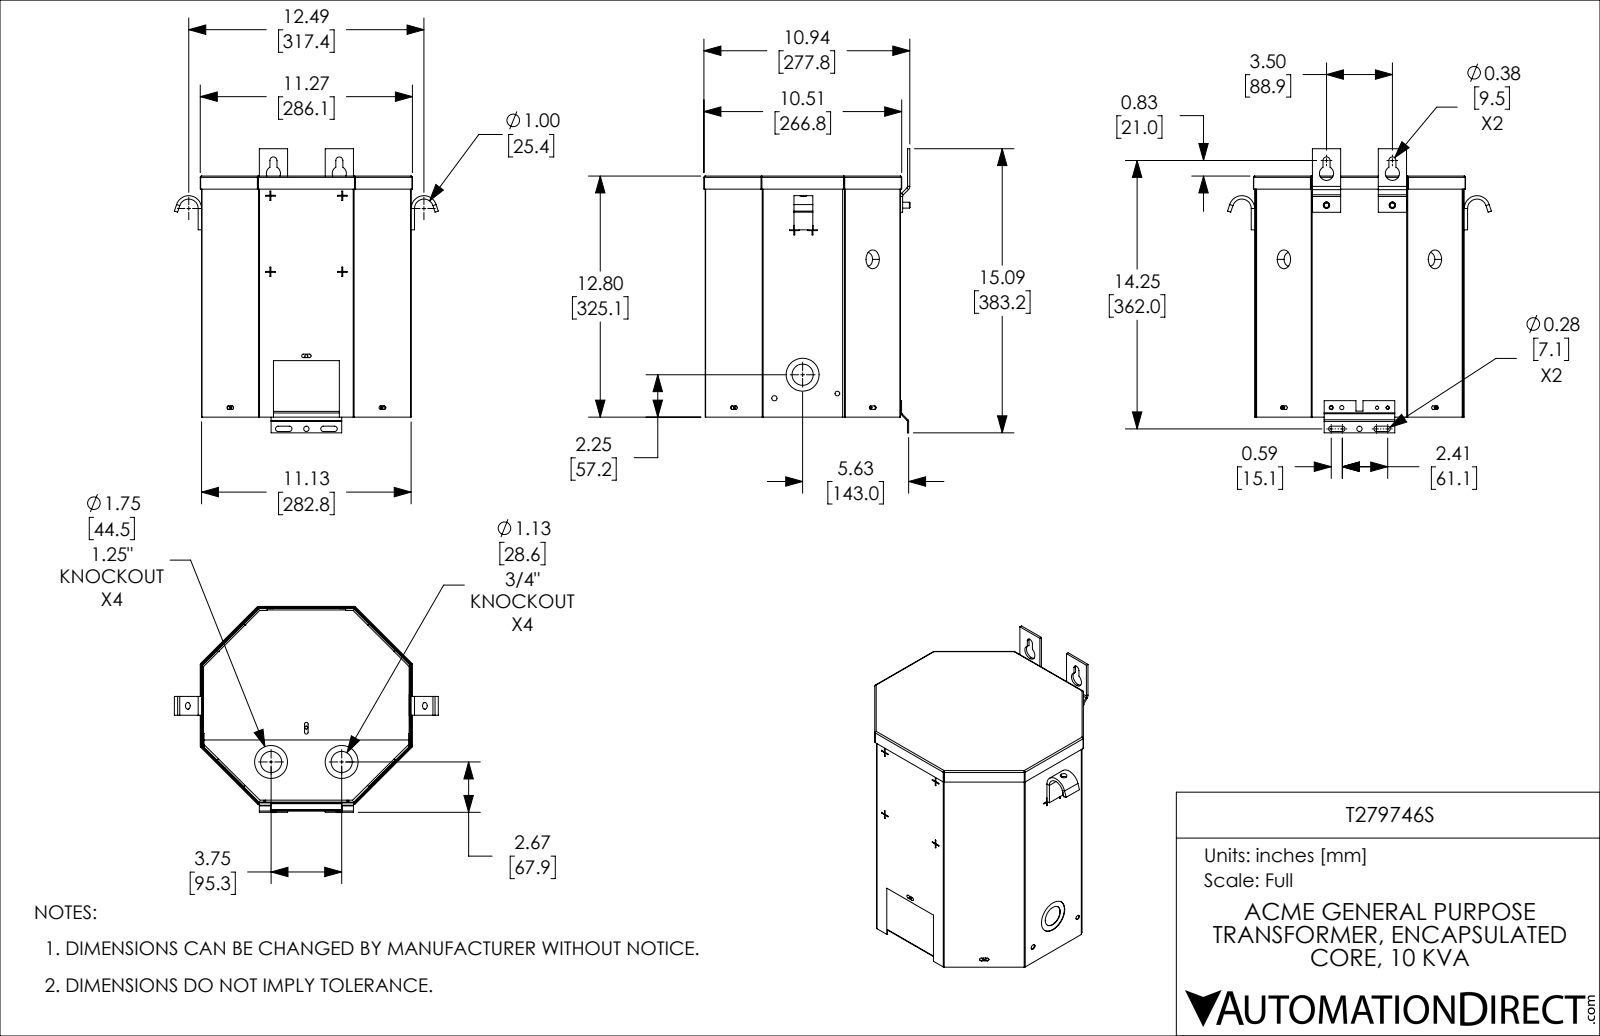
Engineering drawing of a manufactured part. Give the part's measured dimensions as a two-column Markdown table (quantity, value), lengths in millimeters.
| quantity | value |
| --- | --- |
| part name | T279746S |
| STEP written by | SolidWorks 2021 (CONFIG_CONTROL_DESIGN) |
| units | millimeters |
| bodies | 13 solids, 643 faces (422 planar, 185 cylindrical, 36 other) |
| overall size | 383.16 × 356.02 × 278.11 |
| volume | 623 125 mm³ |
| surface area | 974 373 mm² |
| round holes (diameter × count) | 4.04 × 5, 4.06 × 3, 28.58 × 3, 44.45 × 3, 4.37 × 2, 5.56 × 2, 6.35 × 2, 6.5 × 2, 7.14 × 2, 7.92 × 2, 7.94 × 2, 8.73 × 2 |
| round bosses / shafts (diameter × count) | 7.92 × 1 |
| partial cylindrical surfaces (radius × count) | 0.61 × 16, 1.82 × 16, 2.38 × 14, 3.57 × 4, 0.86 × 3, 1.27 × 3, 2.06 × 3, 2.48 × 3 |
| main face-to-face distances | 1.22, 1.21, 275.79, 277, 281.6, 274.58, 1.2, 316.45, 318.21, 319.43 |
| hole center spacings | 88.9, 282.58, 14.29, 61.91, 273.12, 285.26, 0.8, 42.86 |
